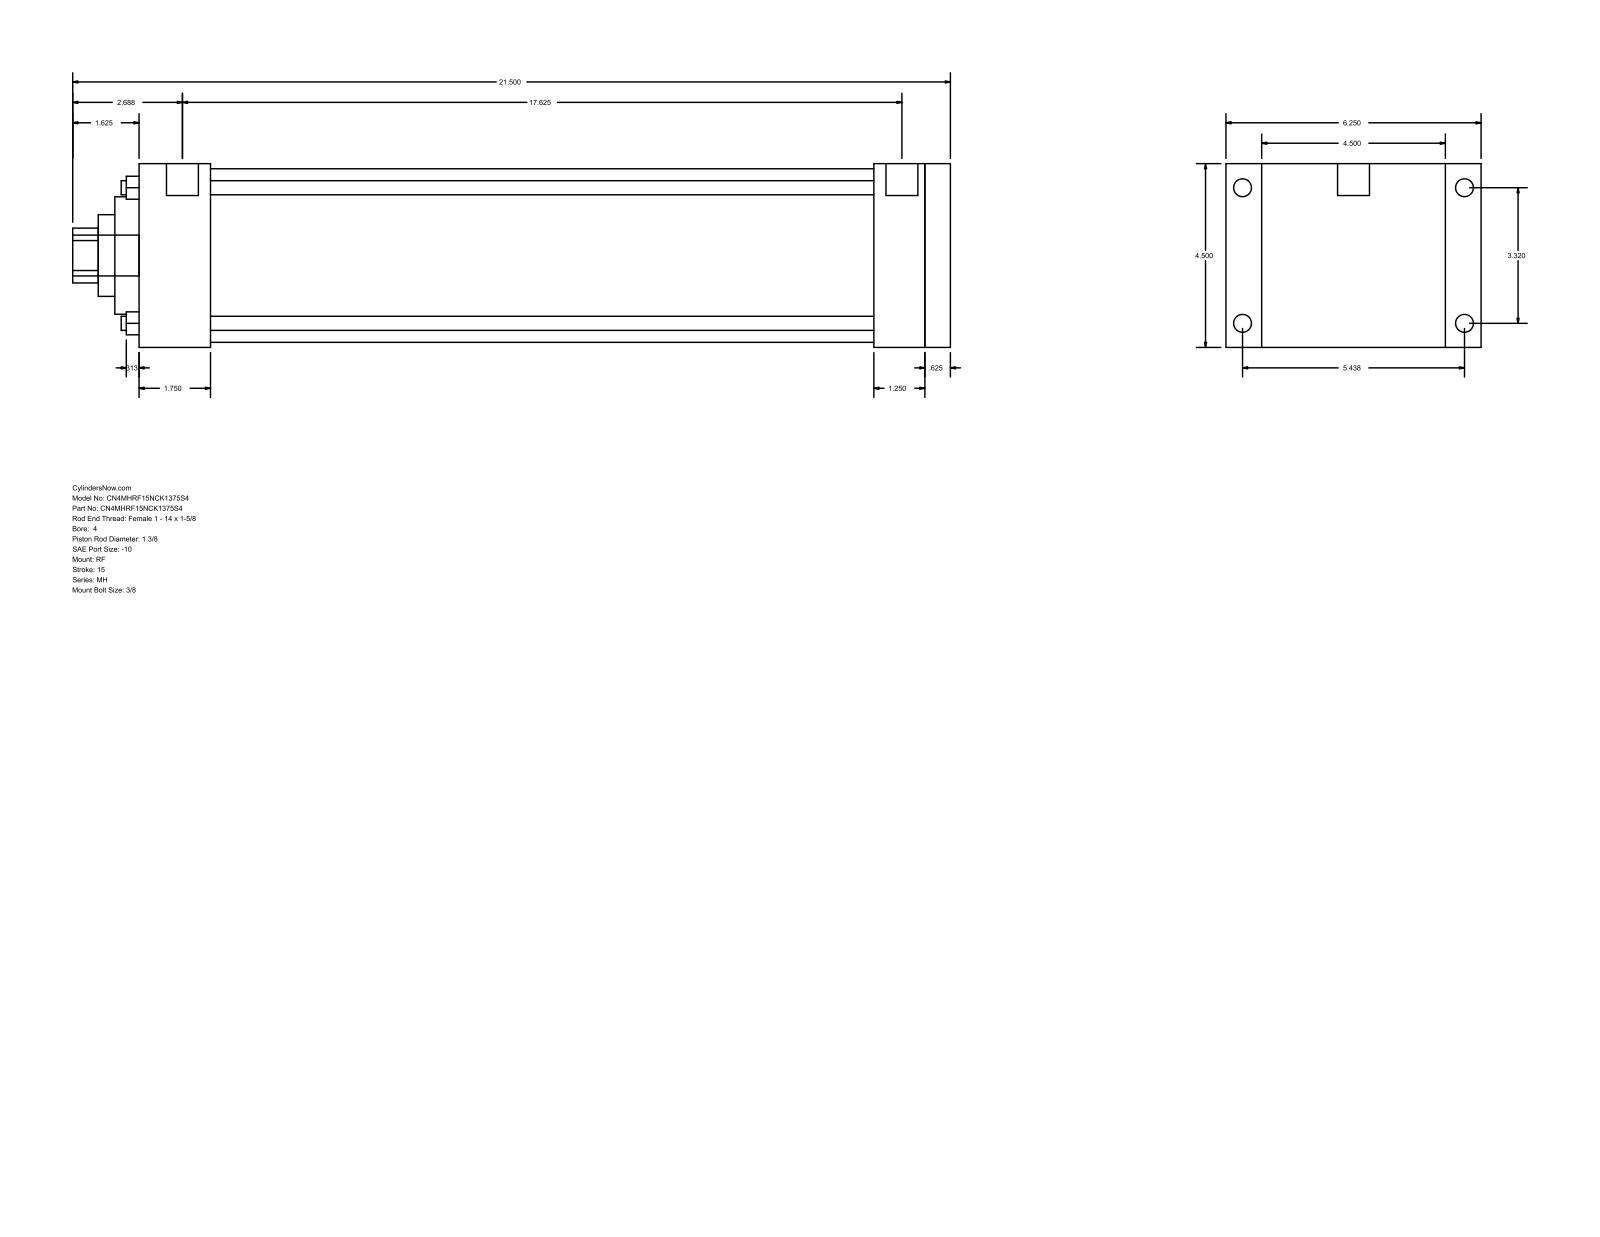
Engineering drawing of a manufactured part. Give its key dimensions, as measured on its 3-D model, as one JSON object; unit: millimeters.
{"part_name": "MH_RF__0400_1.375", "step_written_by": "GSSL Pune (CONFIG_CONTROL_DESIGN)", "units": "millimeters", "bodies": {"solids": 0, "faces": 94, "planar": 65, "cylindrical": 29, "other": 0}, "overall_size": [546.1, 158.75, 114.3], "round_holes": [[8.76, 4], [34.92, 1], [50.8, 1], [73.03, 1], [107.95, 1]], "round_bosses_or_shafts": [[11.13, 4], [8.73, 4], [19.84, 2], [25.4, 1]], "partial_cylinders_radius": [[17.06, 1]], "face_to_face_distances": [114.3, 504.83, 488.96, 15.87, 44.45, 444.51, 460.38, 457.21, 412.76, 31.75], "hole_center_spacings": [59.62, 84.32, 119.25]}
